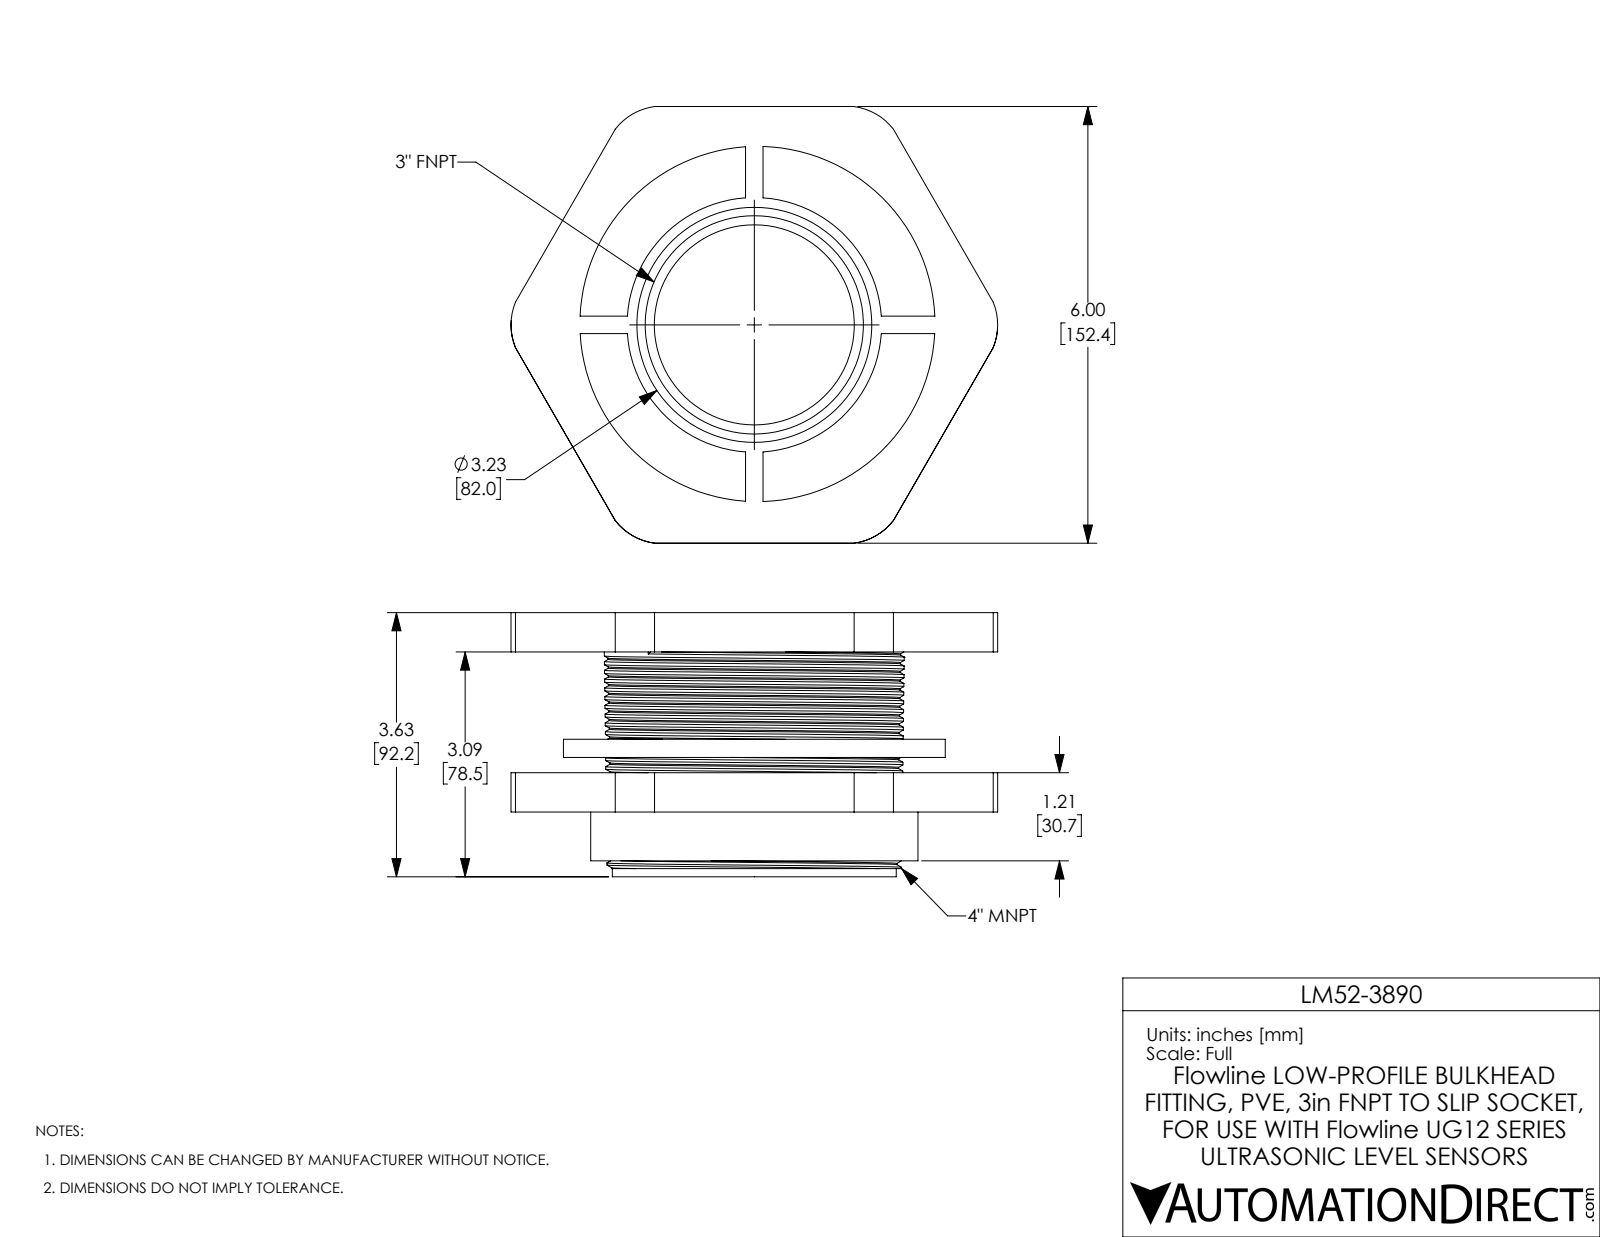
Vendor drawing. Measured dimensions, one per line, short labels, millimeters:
name: LM52-3890
written by: SolidWorks 2017 (AUTOMOTIVE_DESIGN)
unit: mm
bodies: 2 solids, 131 faces (39 planar, 38 cylindrical, 54 other)
size: 170 × 152.5 × 92.2
volume: 710 500 mm³; area: 161 600 mm²
holes: 1× ⌀69.9, 1× ⌀76.2, 1× ⌀82, 1× ⌀103.4, 1× ⌀108, 1× ⌀124
bosses: 1× ⌀133.4, 1× ⌀114.3, 1× ⌀99.2, 1× ⌀88.9
rounds: 12× R20.9
face distances: 13.7, 55.9, 42.2, 69.6, 6.4, 152.4, 44.2, 69, 55.2, 13.1
hole spacings: 1.1
